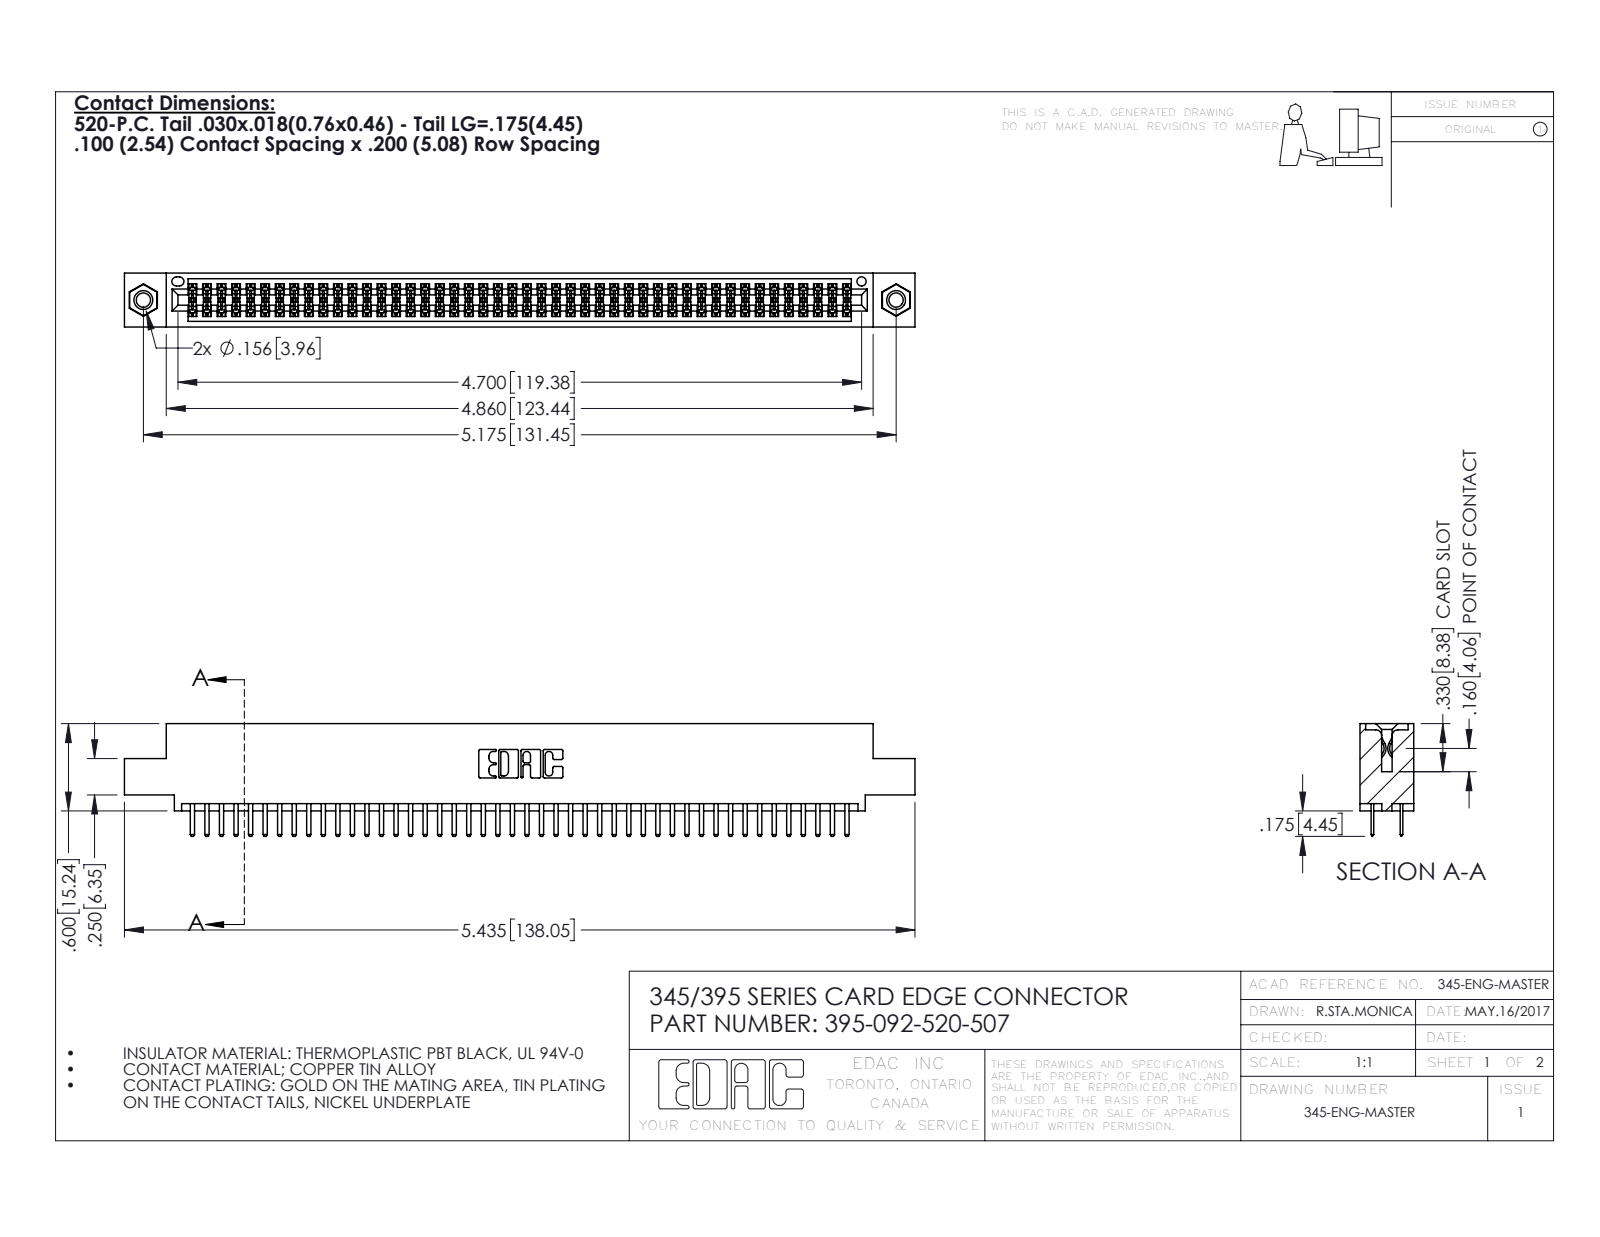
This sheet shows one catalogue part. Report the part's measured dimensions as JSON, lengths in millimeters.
{"part_name": "345-292-001_345-293-120; 345-250-001_345-250-005-103; 345 Part_0.110 Offset - 0.156 Dia-TI; 395-092-520-507", "step_written_by": "SolidWorks 2016 (CONFIG_CONTROL_DESIGN)", "units": "millimeters", "bodies": {"solids": 95, "faces": 5158, "planar": 3336, "cylindrical": 1806, "other": 16}, "overall_size": [138, 19.7, 9.4], "volume_mm3": 13300, "surface_area_mm2": 19800, "round_holes": [[2.5, 2], [3.2, 2], [4, 2], [1.6, 1]], "round_bosses_or_shafts": [[3.9, 2]], "partial_cylinders_radius": [[0.2, 138], [0.3, 96], [0.3, 22], [0.2, 6], [0.8, 6], [0.7, 3], [0.4, 2], [0.5, 2]], "face_to_face_distances": [1.8, 7.6, 5.1, 9.4, 2.5, 6.9, 0.6, 5.7, 0.6, 1.8], "hole_center_spacings": [6.9, 125.5, 131.4]}
